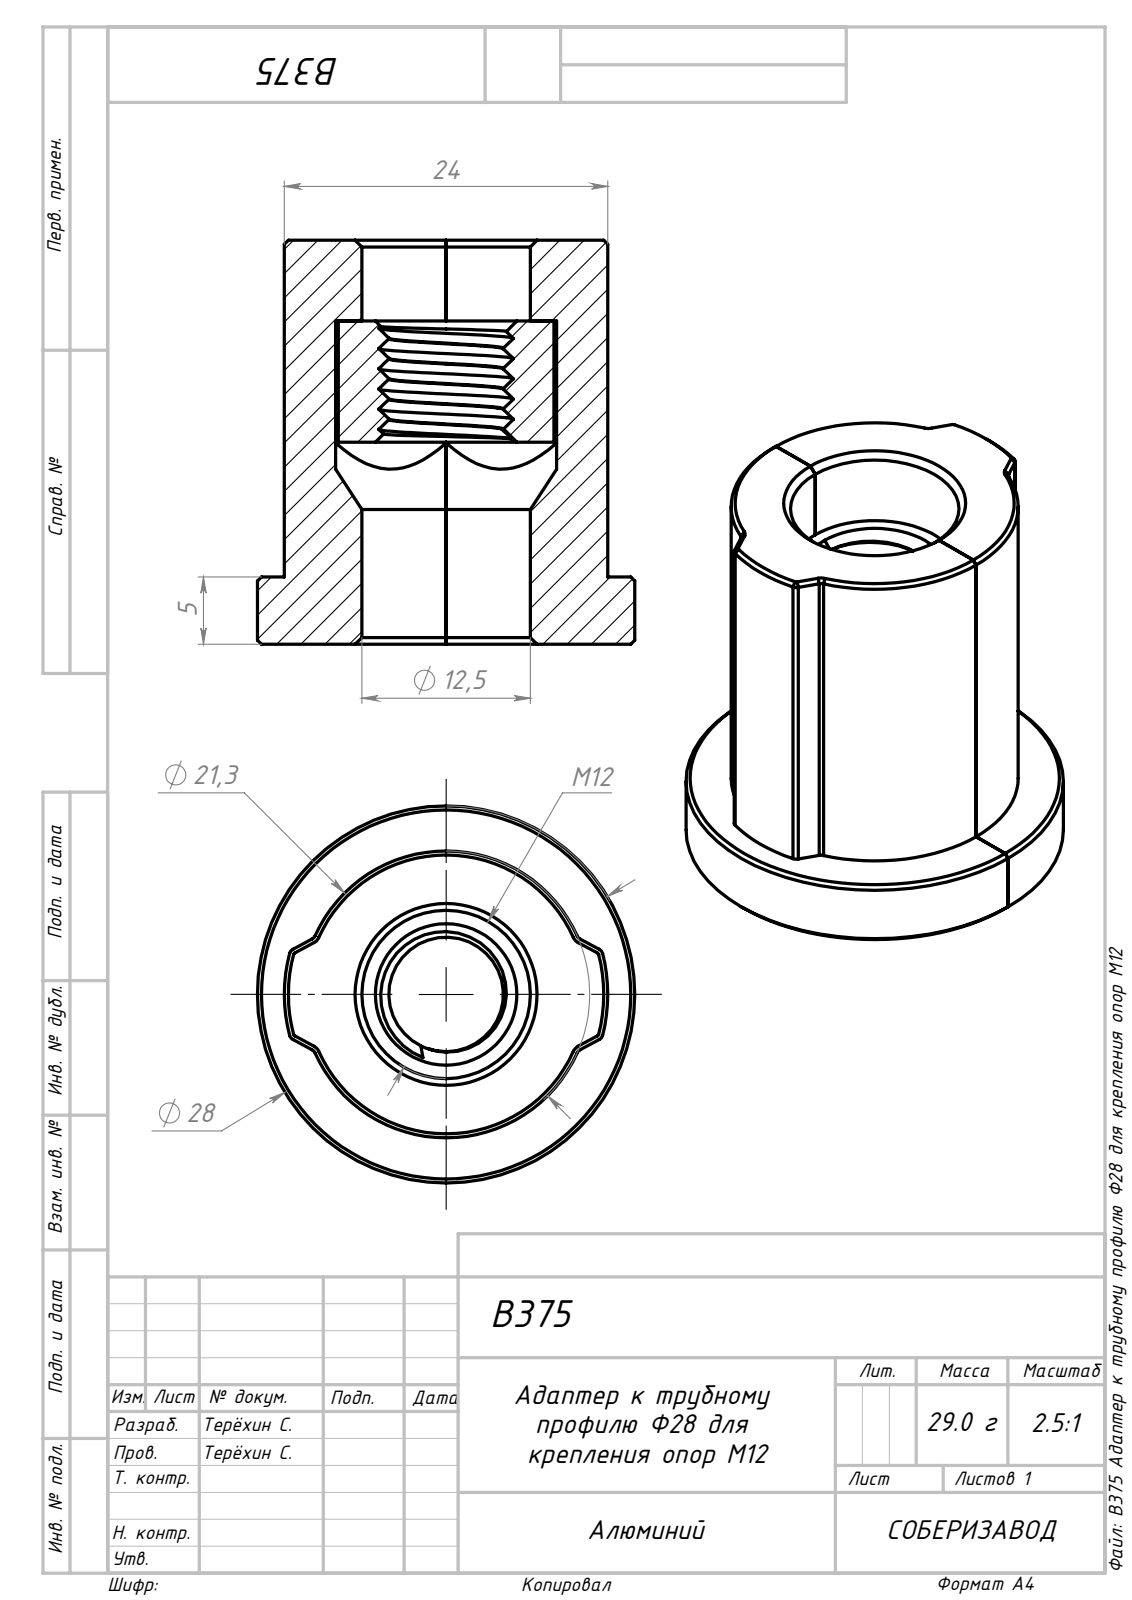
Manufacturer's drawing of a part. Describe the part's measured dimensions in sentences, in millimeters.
The part is named "B375 Адаптер к трубному профилю Ф28 для крепления опор М12". Its 3-D file was written by "SolidWorks 2022 (AUTOMOTIVE_DESIGN)". It is 3 solids with 110 faces: 34 planar, 28 cylindrical and 48 other. Overall it measures 30 by 28 by 28 millimeters. Its volume is 8 838 cubic millimeters and its surface area 6 224 square millimeters. Round holes: 1 of diameter 8.5, 1 of diameter 12.5. Round bosses or shafts: 1 of diameter 28. Partial cylindrical surfaces (rounded edges, fillets, slot ends): 8 of radius 0.5, 1 of radius 10.65, 1 of radius 12. The main face-to-face distances are 16.2, 16.4, 16, 15, 24, 5, 19, 30, 25, 6.
